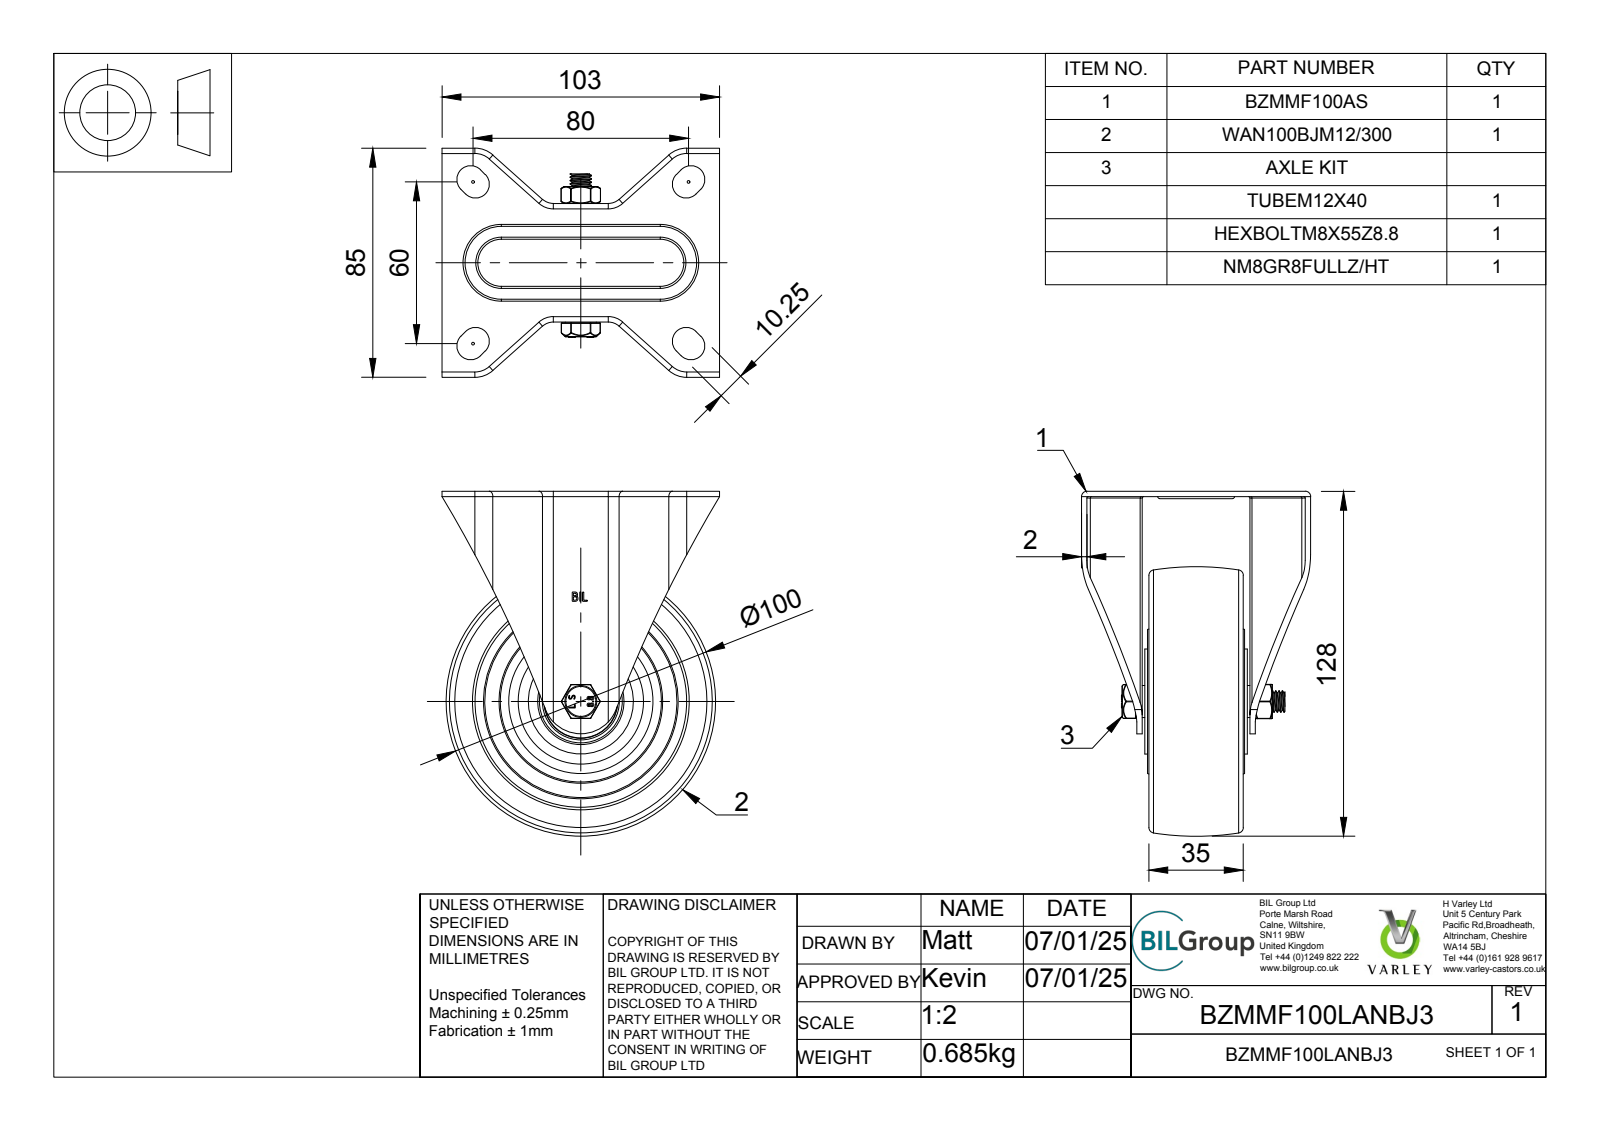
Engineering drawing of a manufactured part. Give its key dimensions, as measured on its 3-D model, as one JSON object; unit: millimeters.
{"part_name": "BZMMF100LANBJ3 v3; BZMMF100AS v1; BZMMF100AS; ZINC PLATED, PRESSED STEEL BRACKET (+7 more)", "step_written_by": "Autodesk Translation Framework v13.20.0.188 (AP242_MANAGED_MODEL_BASED_3D_ENGINEERING_MIM_LF)", "units": "millimeters", "bodies": {"solids": 29, "faces": 583, "planar": 181, "cylindrical": 194, "other": 208}, "overall_size": [128, 103, 85], "volume_mm3": 252034, "surface_area_mm2": 94117, "round_holes": [[0.66, 2], [8, 1], [8.25, 1], [8.4, 1], [12, 1], [18.45, 1], [18.64, 1], [20.6, 1], [26.14, 1], [27.34, 1], [29, 1], [30, 1]], "round_bosses_or_shafts": [[39, 1], [27.14, 1], [26.94, 1], [19.64, 1], [17, 1], [11.9, 1], [11.5, 1], [7.87, 1]], "partial_cylinders_radius": [[0.25, 18], [0.5, 8], [0.75, 8], [2, 8], [5.12, 8], [0.33, 4], [0.64, 4], [3, 4]], "face_to_face_distances": [2, 14.26, 2.5, 37.5, 4.5, 39.5, 42, 40, 12.26, 29], "hole_center_spacings": [3.22, 2.49]}
